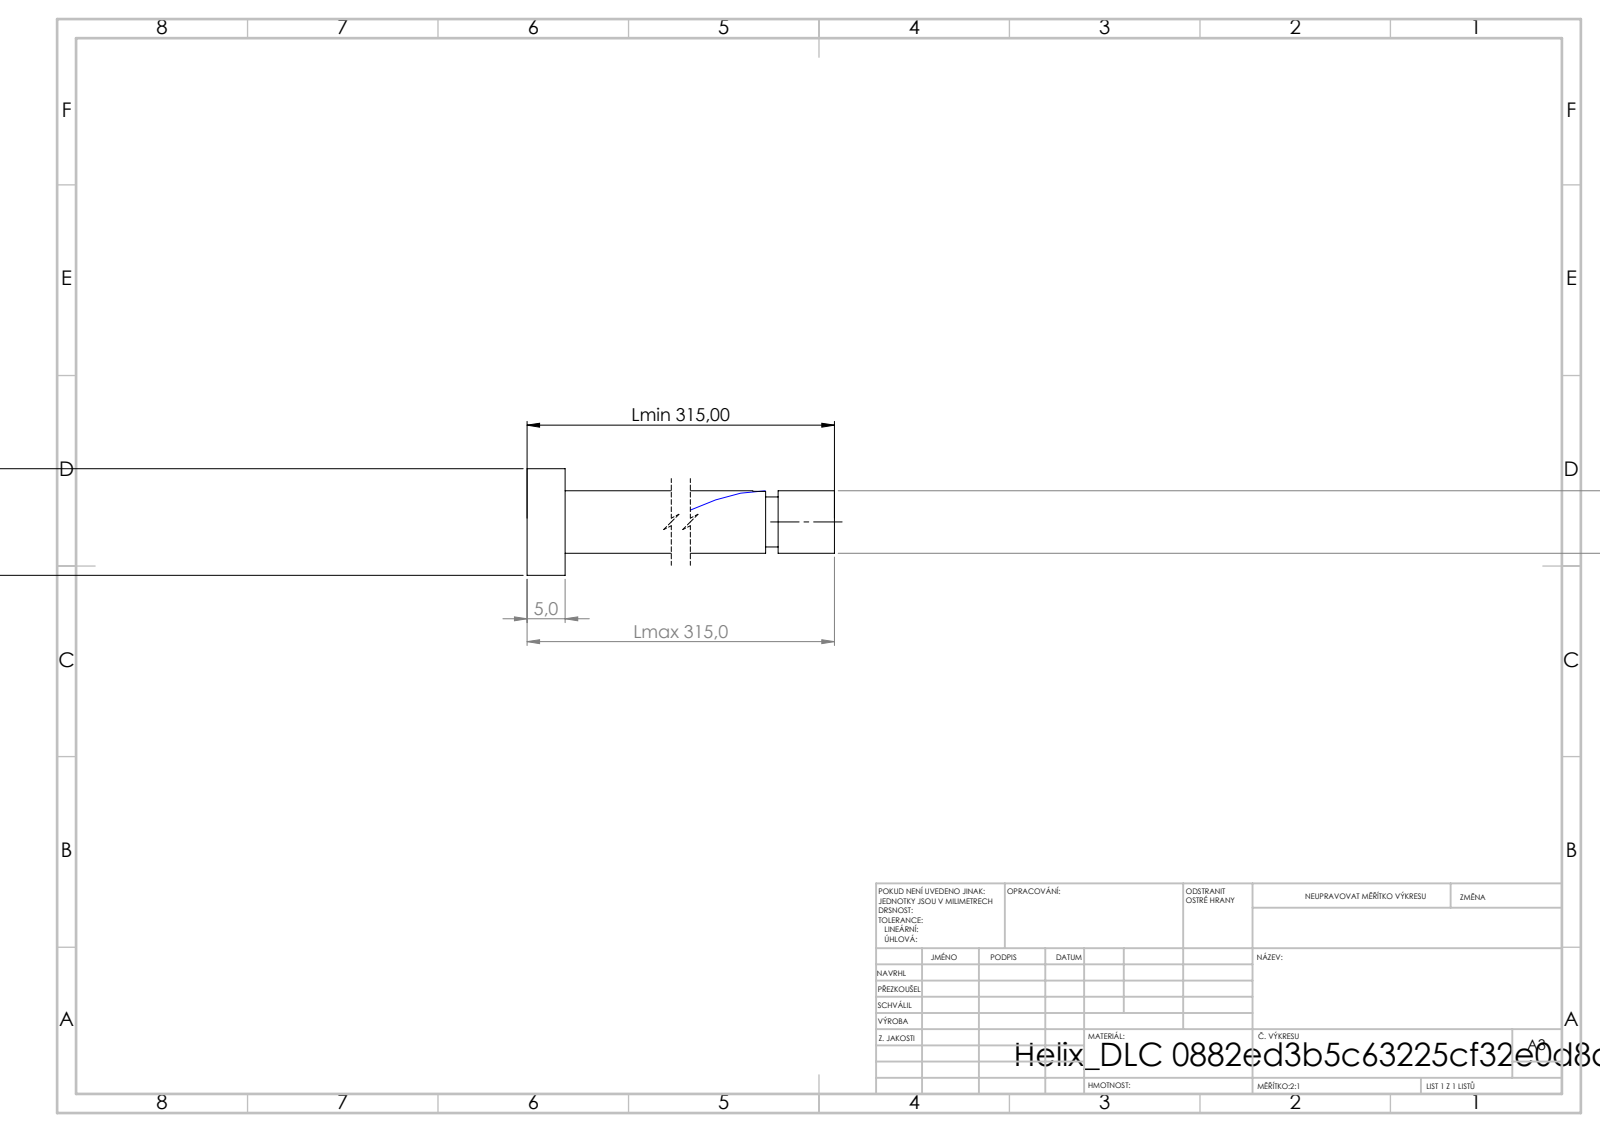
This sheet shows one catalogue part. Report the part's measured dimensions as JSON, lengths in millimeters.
{"step_written_by": "SolidWorks 2019 (CONFIG_CONTROL_DESIGN)", "units": "millimeters", "bodies": {"solids": 1, "faces": 21, "planar": 6, "cylindrical": 14, "other": 1}, "overall_size": [315, 14, 14], "volume_mm3": 16950, "surface_area_mm2": 8685, "round_bosses_or_shafts": [[14, 1], [8.2, 1], [6.56, 1]], "face_to_face_distances": [5, 315, 310, 307.61, 302.61, 7.39, 305.97, 300.97, 1.64, 9.03]}
